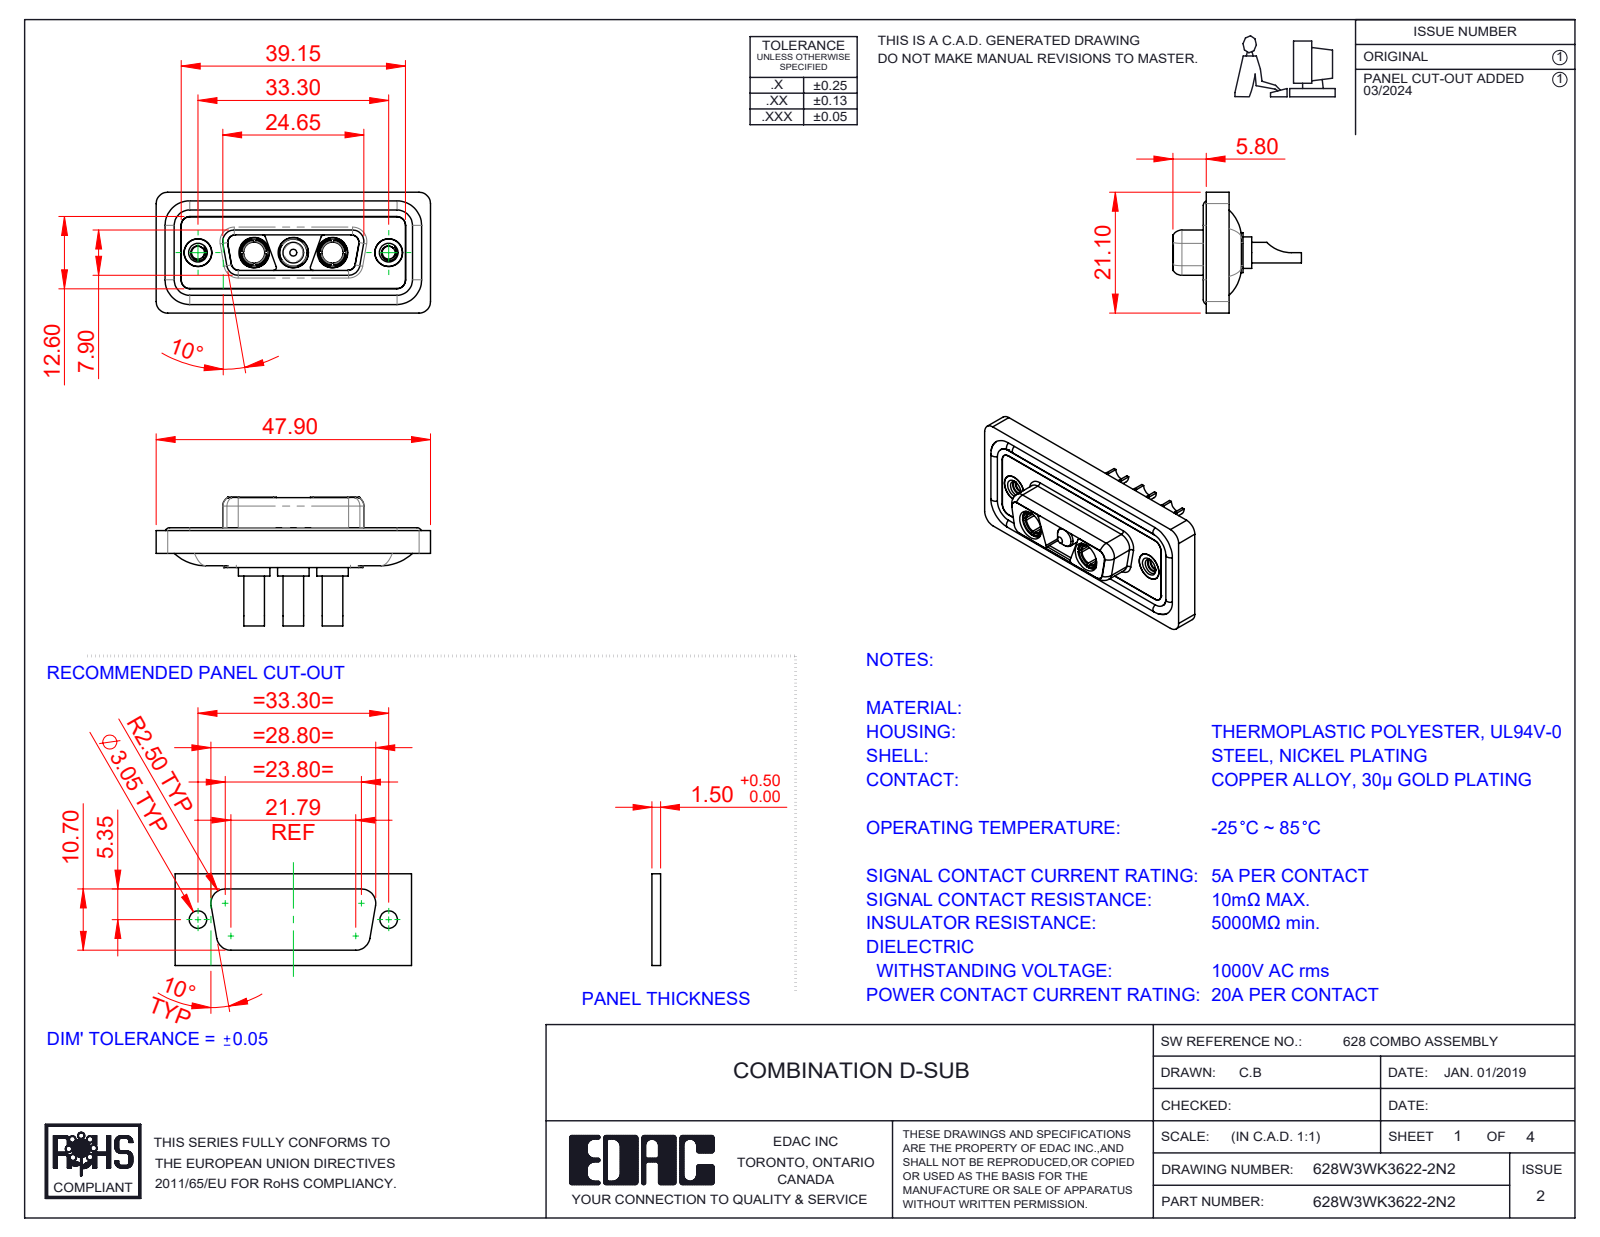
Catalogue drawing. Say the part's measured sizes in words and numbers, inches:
The part is named "628Combo Housing_3WK3; Power Pin_20A SC; 628Combo Waterproof Housing_15 Contacts; 628W3WK3622-2N2 (+4 more)". Its 3-D file was written by "SolidWorks 2023 (CONFIG_CONTROL_DESIGN)". It is 13 solids with 602 faces: 187 planar, 267 cylindrical and 148 other. Overall it measures 1.886 by 0.884 by 0.831 inches. Its volume is 0.361 cubic inches and its surface area 15.12 square inches. Round holes: 5 of diameter 0.191, 3 of diameter 0.106, 3 of diameter 0.209, 2 of diameter 0.089, 2 of diameter 0.146, 2 of diameter 0.157, 2 of diameter 0.159, 2 of diameter 0.197. Round bosses or shafts: 4 of diameter 0.063, 3 of diameter 0.217, 3 of diameter 0.205, 3 of diameter 0.187, 3 of diameter 0.148, 3 of diameter 0.142, 2 of diameter 0.195, 2 of diameter 0.195. Partial cylindrical surfaces (rounded edges, fillets, slot ends): 22 of radius 0.059, 20 of radius 0.079, 12 of radius 0.053, 8 of radius 0.02, 8 of radius 0.063, 4 of radius 0.01, 4 of radius 0.024, 4 of radius 0.026. The main face-to-face distances are 0.016, 0.063, 0.02, 0.071, 0.043, 0.114, 0.222, 0.278, 0.211, 0.059. The hole center spacings are 0.27, 0.386, 0.656, 0.925, 0.539, 1.311.
